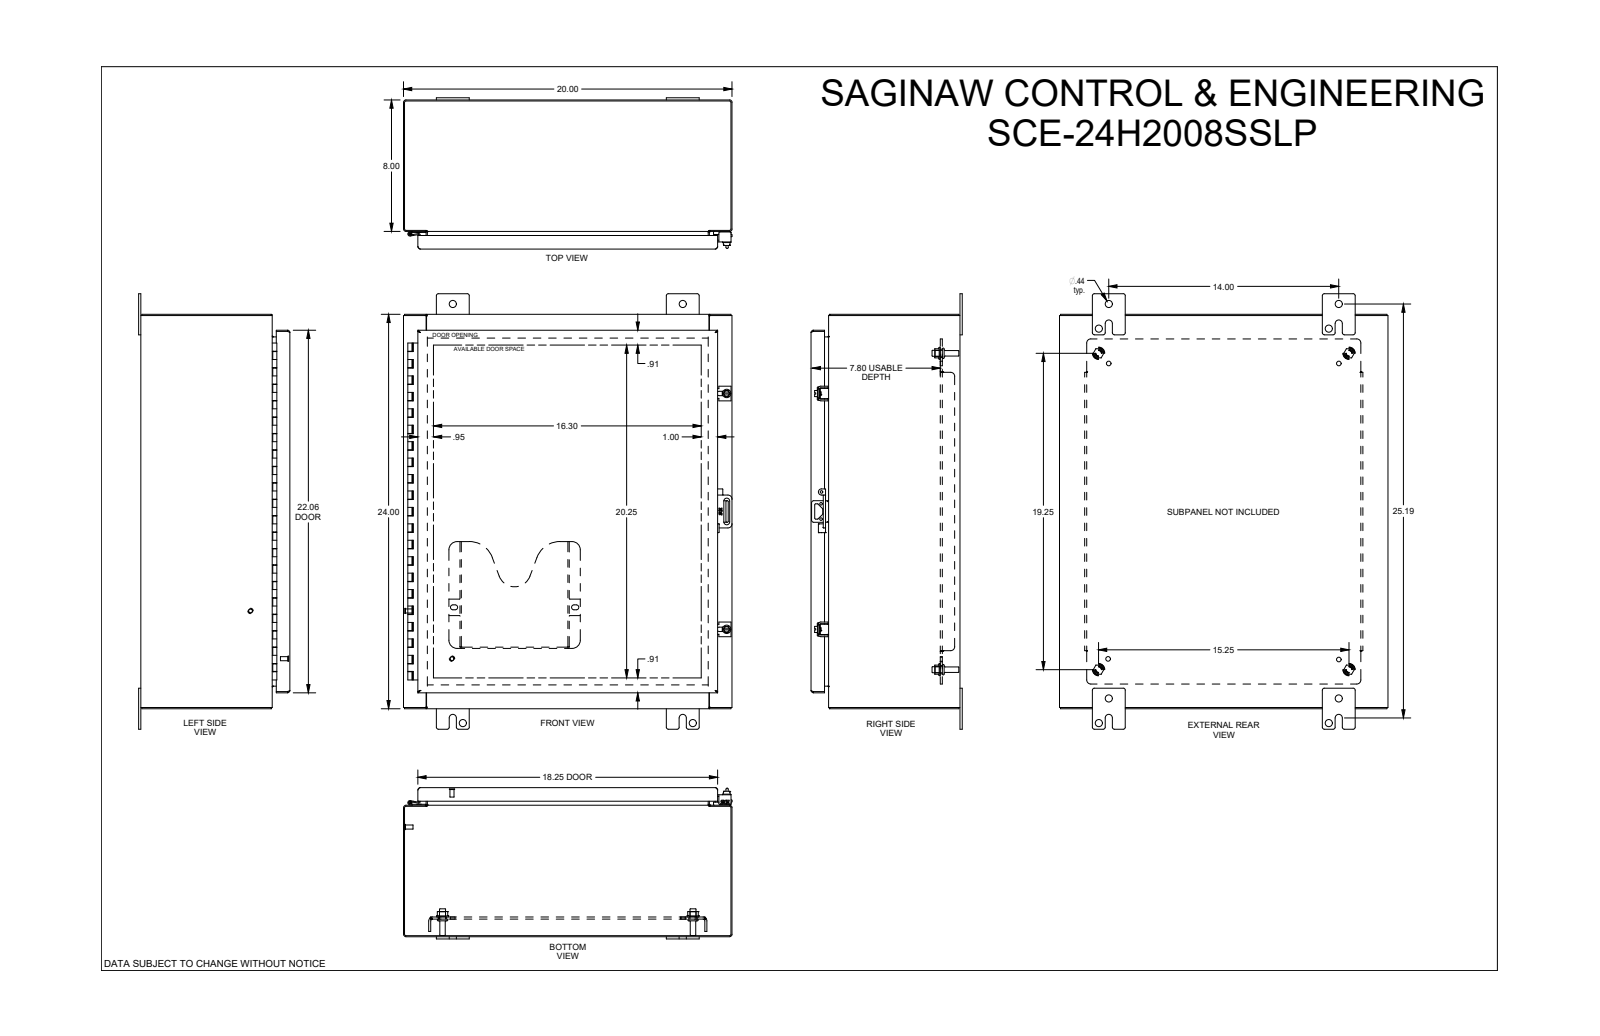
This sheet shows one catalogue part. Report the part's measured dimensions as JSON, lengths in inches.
{"part_name": "SCE-24H2008SSLP", "step_written_by": "SolidWorks 2019 (CONFIG_CONTROL_DESIGN)", "units": "inches", "bodies": {"solids": 0, "faces": 3160, "planar": 1275, "cylindrical": 660, "other": 1225}, "overall_size": [26.5, 20, 9.208], "round_holes": [[0.437, 8], [0.25, 5], [0.19, 4], [0.193, 4], [0.281, 4], [0.367, 4], [0.5, 4], [0.16, 2], [0.203, 2], [0.13, 1], [0.132, 1]], "round_bosses_or_shafts": [[0.248, 7], [0.563, 5], [0.366, 4], [0.332, 4], [0.256, 4], [0.188, 4], [0.25, 3], [0.507, 2]], "partial_cylinders_radius": [[0.01, 114], [0.015, 36], [0.029, 30], [0.03, 27], [0.125, 27], [0.06, 25], [0.04, 22], [0.07, 14]], "face_to_face_distances": [0.075, 0.075, 8.998, 8.923, 8.998, 9.073, 19.925, 7.923, 1.2, 1.125], "hole_center_spacings": [0.875, 14, 6.5, 14.644, 18.641, 23.689, 0.515, 1.439]}
